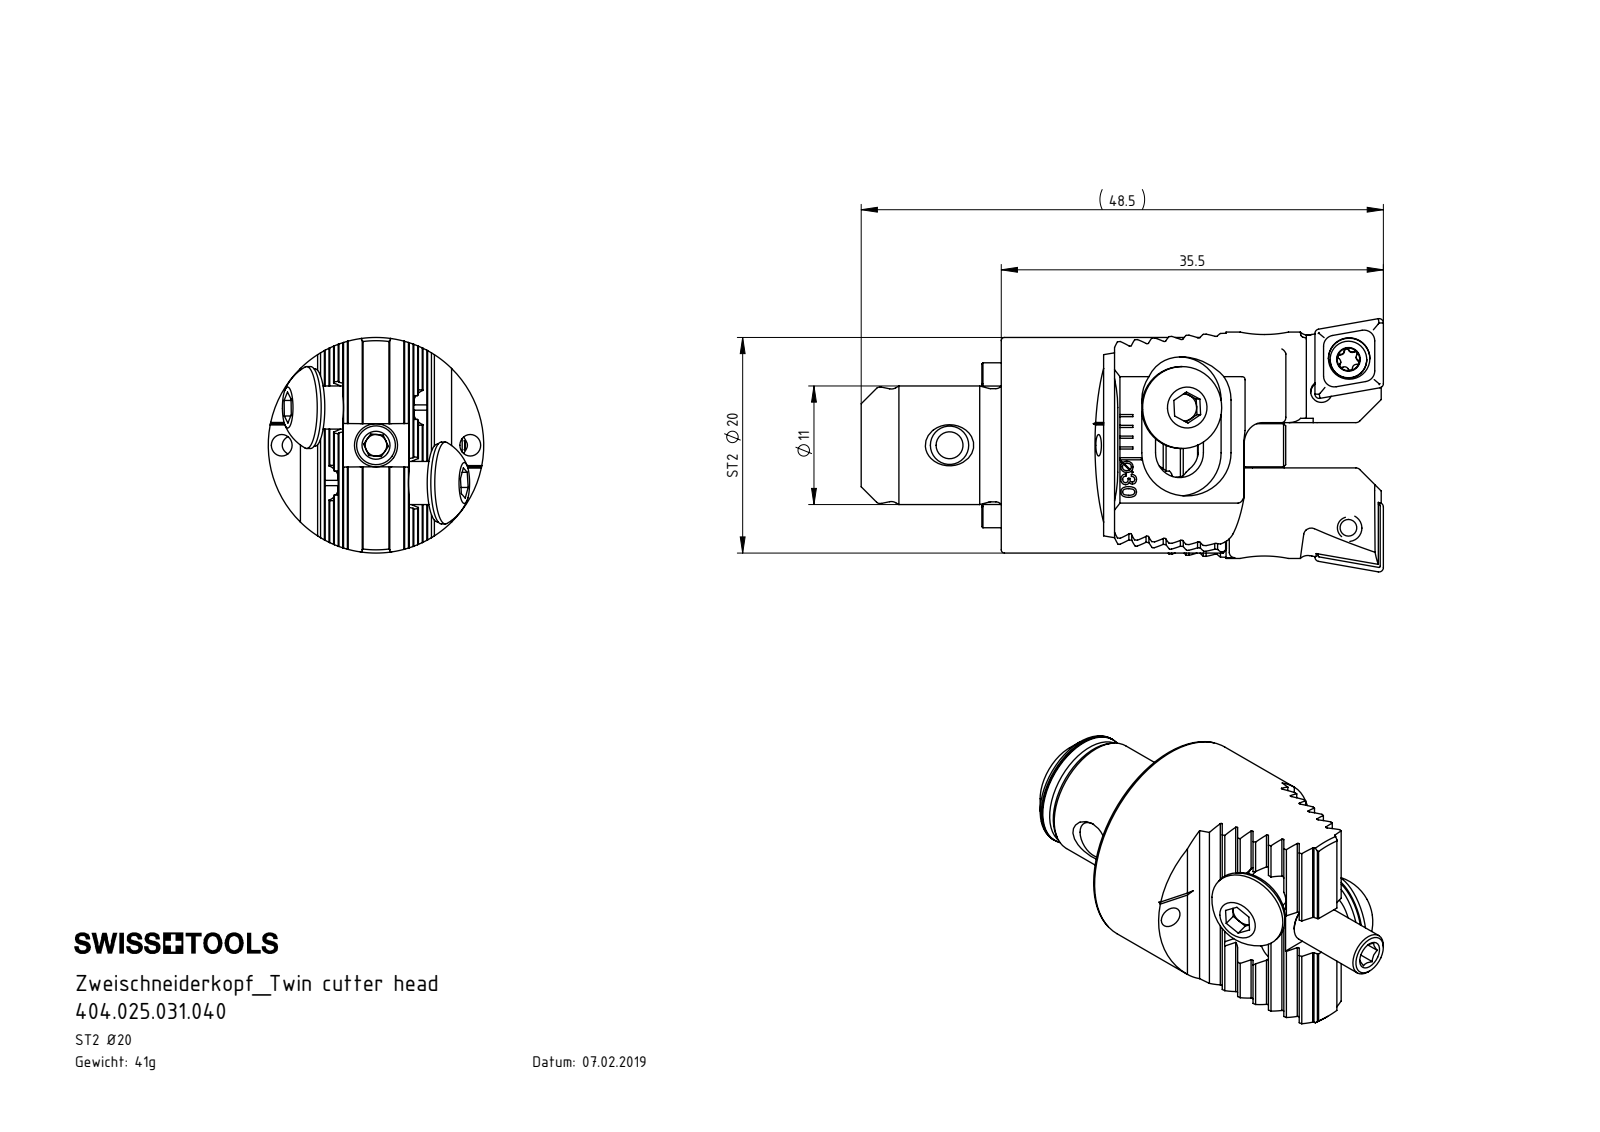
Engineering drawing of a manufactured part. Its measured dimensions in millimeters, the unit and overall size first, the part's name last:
Units: millimetres
Overall size (bounding box): 56 × 29.5 × 25
Round holes (diameter × count): ⌀2.5 ×4, ⌀2 ×3, ⌀1.6 ×2, ⌀2.05 ×2, ⌀2.2 ×2, ⌀2.8 ×2, ⌀3.85 ×2, ⌀4.2 ×2, ⌀5.3 ×2, ⌀6 ×2, ⌀3.3 ×1, ⌀3.5 ×1
Round bosses / shafts (diameter × count): ⌀9.5 ×2, ⌀9.2 ×2, ⌀5 ×2, ⌀4 ×2, ⌀3.4 ×2, ⌀2.5 ×2, ⌀2.2 ×2, ⌀25 ×1
Partial cylindrical surfaces — rounded edges, fillets, slot ends (radius × count): R0.5 ×22, R0.12 ×18, R0.12 ×16, R0.21 ×12, R0.36 ×10, R2 ×4, R2.8 ×4, R5 ×4
Main face-to-face distances: 1.43, 2.86, 1.39, 4.29, 1.47, 5.72, 2.82, 8.57, 7.15, 7.14
Hole centre spacings: 3.91, 4.01, 7, 8.38, 19.06, 19.15, 21.97, 9.3
Volume: 15 499 mm³ · Surface area: 10 594 mm²
Bodies: 17 solids, 1057 faces (486 planar, 267 cylindrical, 304 other)
Part name (STEP PRODUCT): Z25-ER1.003.012_A_gespannt; Z25-ER1.002.012_A; ST2-Z25.K23.040_A; Z25-ER3.001.010_A (+8 more)
STEP written by: SolidWorks 2017 (CONFIG_CONTROL_DESIGN)
